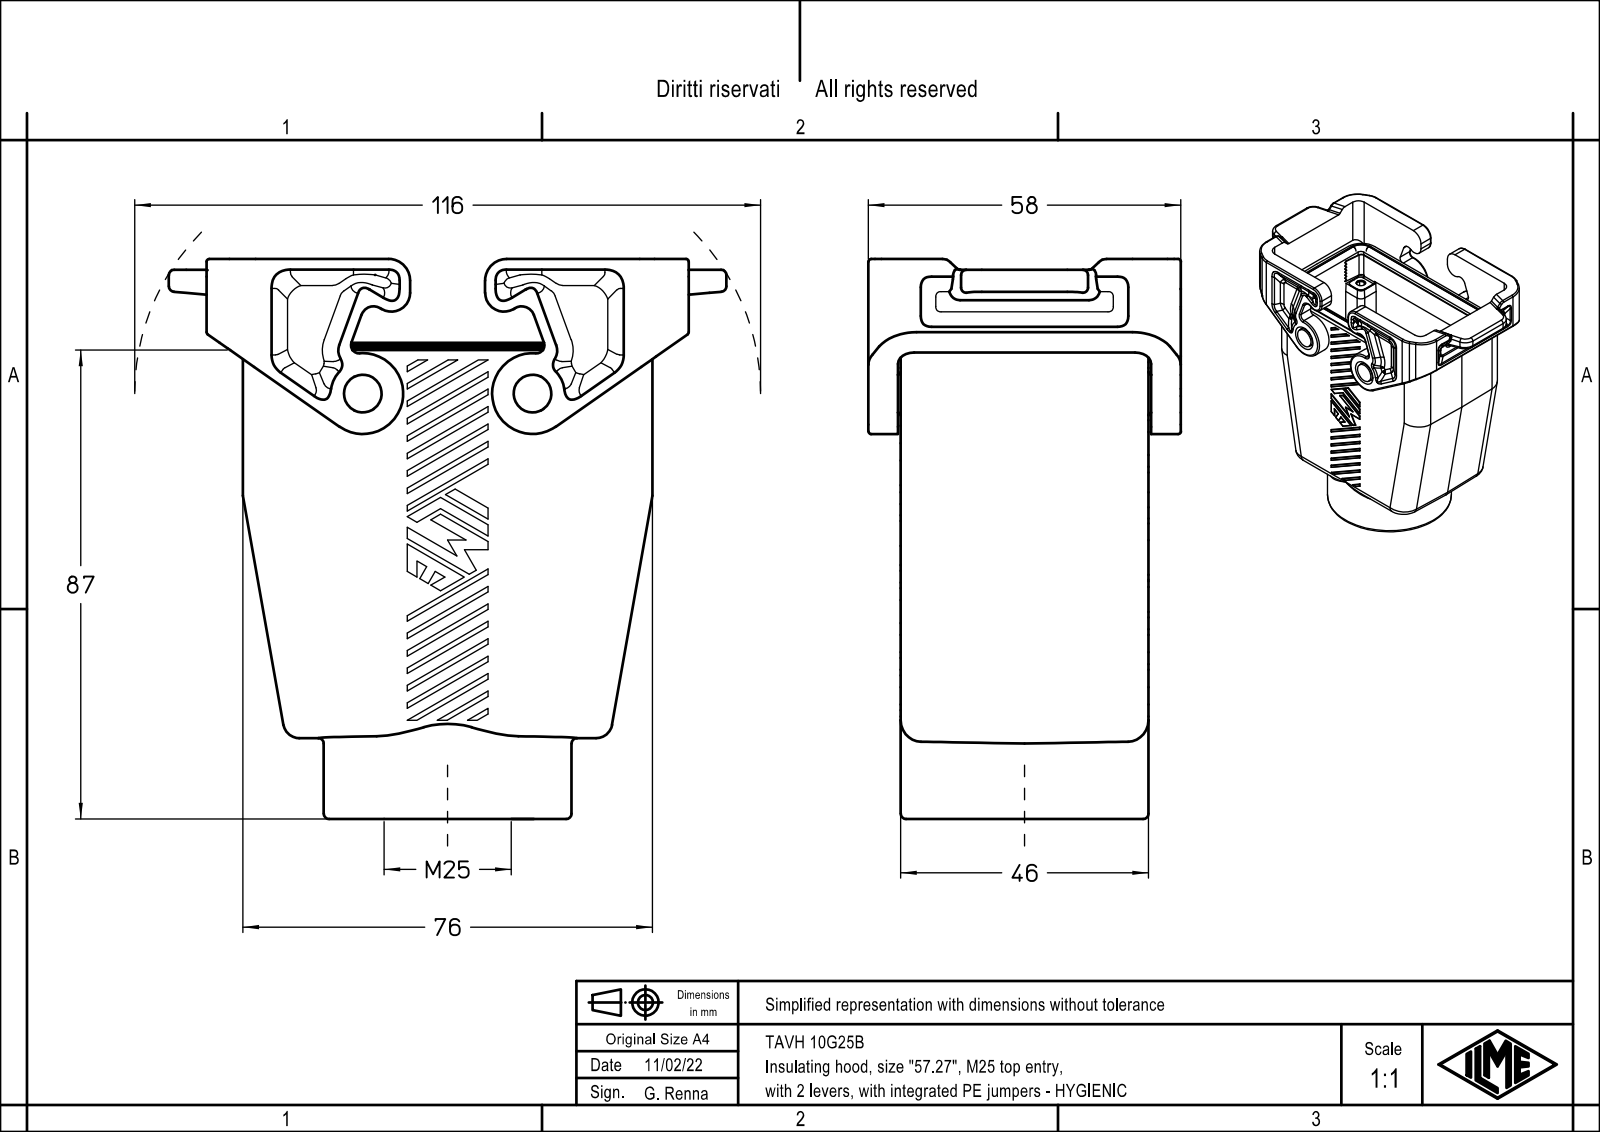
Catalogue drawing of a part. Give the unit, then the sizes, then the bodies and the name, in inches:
Units: inches
Overall size (bounding box): 4.091 × 4.075 × 2.283
Round holes (diameter × count): ⌀0.138 ×4, ⌀0.827 ×1, ⌀0.929 ×1
Round bosses / shafts (diameter × count): ⌀0.276 ×2, ⌀1.811 ×1
Partial cylindrical surfaces — rounded edges, fillets, slot ends (radius × count): R0.006 ×128, R0.079 ×20, R0.118 ×20, R0.059 ×18, R0.039 ×16, R0.051 ×12, R0.236 ×8, R0.276 ×8
Main face-to-face distances: 0.213, 1.598, 1.811, 1.386, 0.02, 0.232, 1.618, 1.831, 0.217, 2.067
Hole centre spacings: 1.242, 1.063, 2.244, 2.483
Volume: 8.548 in³ · Surface area: 84 in²
Bodies: 1 solid, 856 faces (396 planar, 398 cylindrical, 62 other)
Part name (STEP PRODUCT): TAVH 10 G25
STEP written by: Creo Elements/Direct Modeling 20.1B 02-Apr-2019 (C) Parametric Technology GmbH (AUTOMOTIVE_DESIGN)
